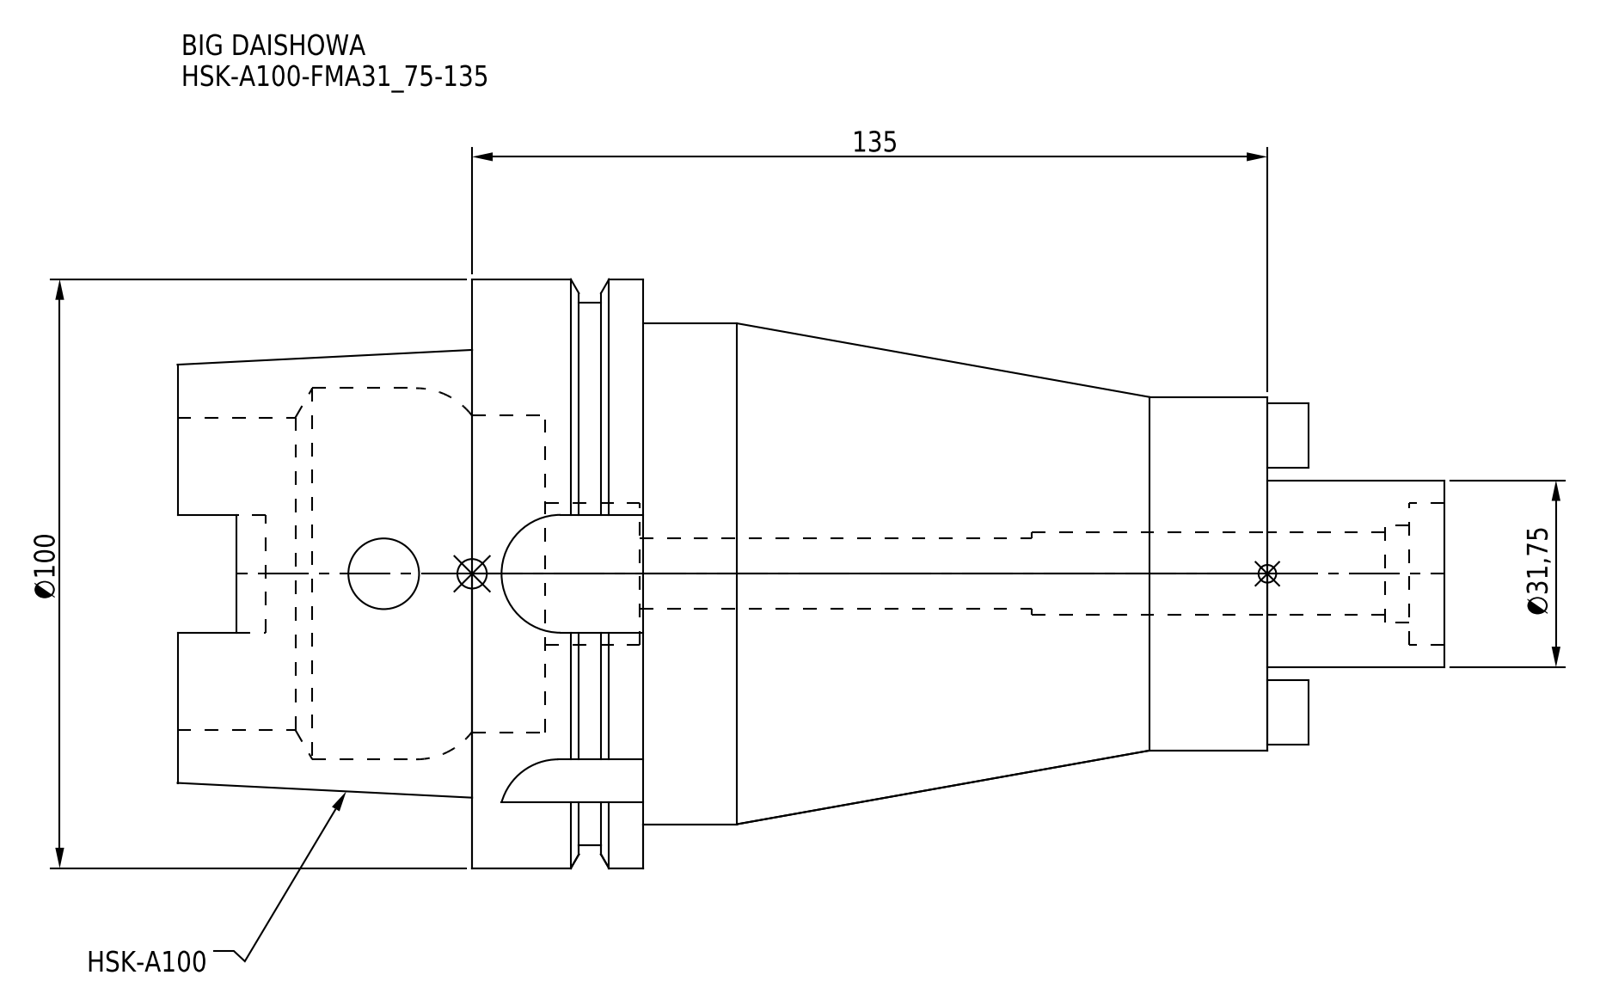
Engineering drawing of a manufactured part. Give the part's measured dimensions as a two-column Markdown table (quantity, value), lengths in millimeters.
| quantity | value |
| --- | --- |
| part name | HSK-A100-FMA31_75-135 |
| STEP written by | CREO PARAMETRIC BY PTC INC, 2016380 (AUTOMOTIVE_DESIGN) |
| units | millimeters |
| bodies | 1 solid, 108 faces (46 planar, 46 cylindrical, 16 other) |
| overall size | 215 × 100 × 100 |
| volume | 698 053 mm³ |
| surface area | 80 622 mm² |
| round holes (diameter × count) | 12 × 2, 14 × 1, 16.5 × 1, 24 × 1, 53 × 1, 53.8 × 1, 63 × 1 |
| round bosses / shafts (diameter × count) | 100 × 1, 92 × 1, 85 × 1, 60 × 1, 31.75 × 1 |
| partial cylindrical surfaces (radius × count) | 4.88 × 4, 10 × 4 |
| main face-to-face distances | 29, 16.55, 12.45, 135, 106, 122.55, 185, 79, 62.45, 50 |
